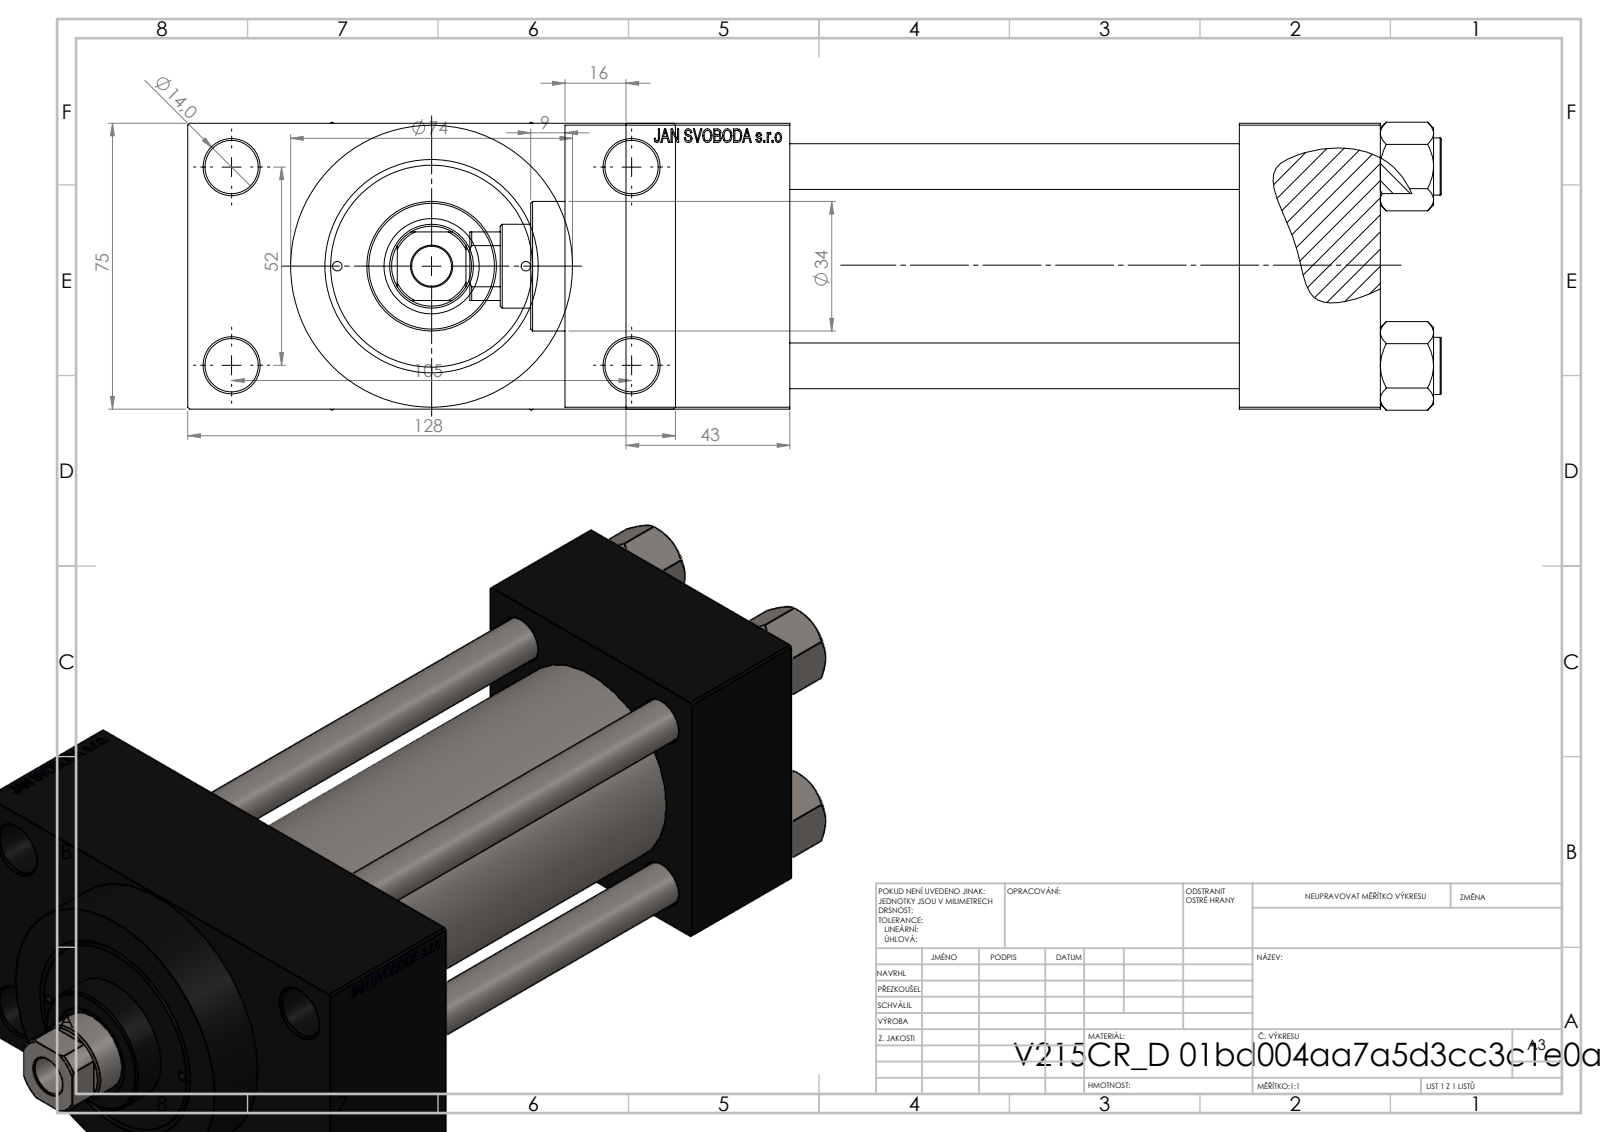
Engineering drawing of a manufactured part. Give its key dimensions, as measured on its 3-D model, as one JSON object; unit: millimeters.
{"part_name": "NUT_M5_D; V215_VC_A; V215CR_VCP_D; V215CR_D_Body (+1 more)", "step_written_by": "SolidWorks 2019 (CONFIG_CONTROL_DESIGN)", "units": "millimeters", "bodies": {"solids": 11, "faces": 1111, "planar": 499, "cylindrical": 92, "other": 520}, "overall_size": [255, 128, 75.54], "volume_mm3": 877200, "surface_area_mm2": 199797, "round_holes": [[12, 4], [14, 4], [2.5, 2], [7, 2], [20.96, 2], [30, 2], [10.5, 1], [22, 1], [25, 1], [41, 1], [50, 1], [53, 1]], "round_bosses_or_shafts": [[15, 4], [74, 1], [56, 1], [34, 1]], "partial_cylinders_radius": [[10.5, 1]], "face_to_face_distances": [75, 118, 37, 155, 26.5, 198, 161, 43, 101.5, 16], "hole_center_spacings": [26.19, 26.35, 36.98, 38.03, 52.3, 57.22, 58.43, 58.59]}
